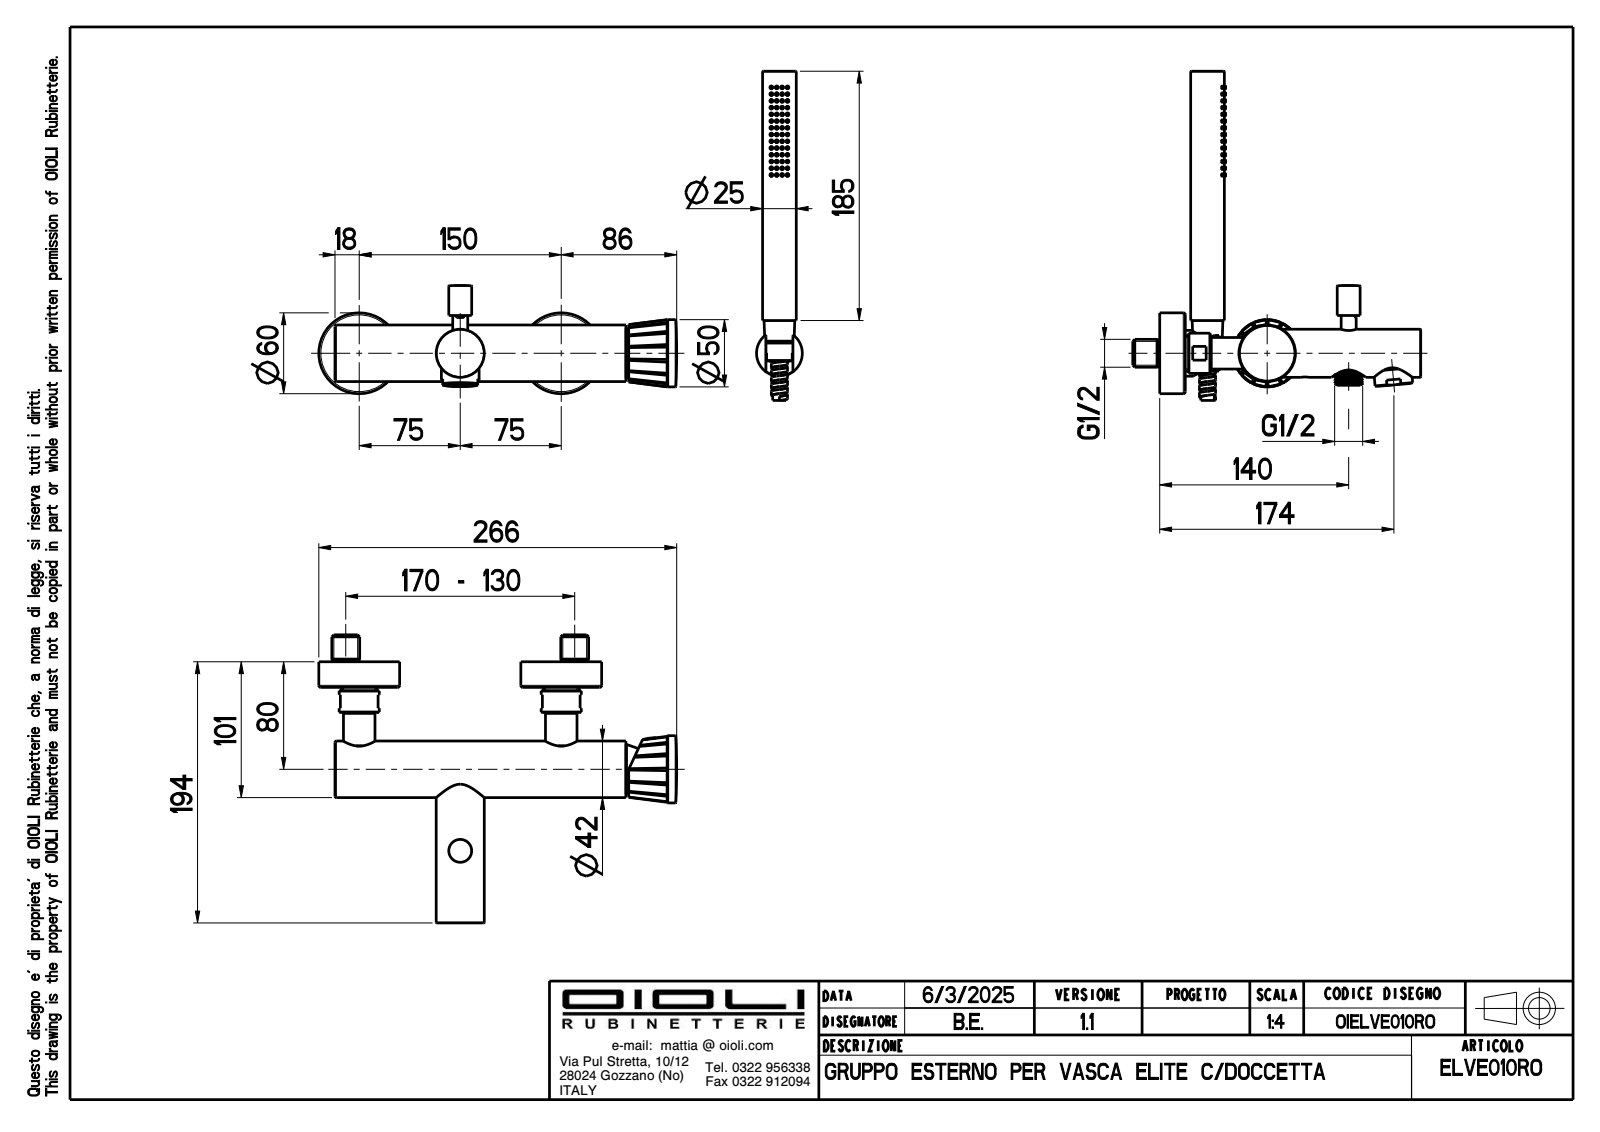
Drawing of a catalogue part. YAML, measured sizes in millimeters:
part_name: "OIBR00305; OIAQ00285; OIBR00998; OIBR00272 (+8 more)"
step_written_by: "CREO PARAMETRIC BY PTC INC, 2024493 (CONFIG_CONTROL_DESIGN)"
units: millimeters
bodies: {solids: 25, faces: 1548, planar: 318, cylindrical: 593, other: 637}
overall_size: [359, 244.3, 213.8]
volume: 515997
surface_area: 202578
round_holes:
  - {diameter: 5, count: 5}
  - {diameter: 7, count: 5}
  - {diameter: 4, count: 3}
  - {diameter: 8, count: 3}
  - {diameter: 10, count: 3}
  - {diameter: 15.5, count: 3}
  - {diameter: 19, count: 3}
  - {diameter: 8.8, count: 2}
  - {diameter: 10.5, count: 2}
  - {diameter: 15, count: 2}
  - {diameter: 16.7, count: 2}
  - {diameter: 19.1, count: 2}
round_bosses_or_shafts:
  - {diameter: 26.4, count: 3}
  - {diameter: 18, count: 3}
  - {diameter: 60, count: 2}
  - {diameter: 29.8, count: 2}
  - {diameter: 27.2, count: 2}
  - {diameter: 26.2, count: 2}
  - {diameter: 23.4, count: 2}
  - {diameter: 23.2, count: 2}
partial_cylinders:
  - {radius: 0.1, count: 10}
  - {radius: 0.5, count: 8}
  - {radius: 1, count: 8}
  - {radius: 7.5, count: 4}
  - {radius: 10, count: 2}
  - {radius: 5.38, count: 1}
  - {radius: 5.47, count: 1}
  - {radius: 5.53, count: 1}
face_to_face_distances: [0.7, 250.6, 16.2, 175.5, 174.8, 15.5, 182.5, 68.1, 13, 8]
hole_center_spacings: [6.28, 8, 8.6, 10, 13.45, 15.13, 21.93, 75]
